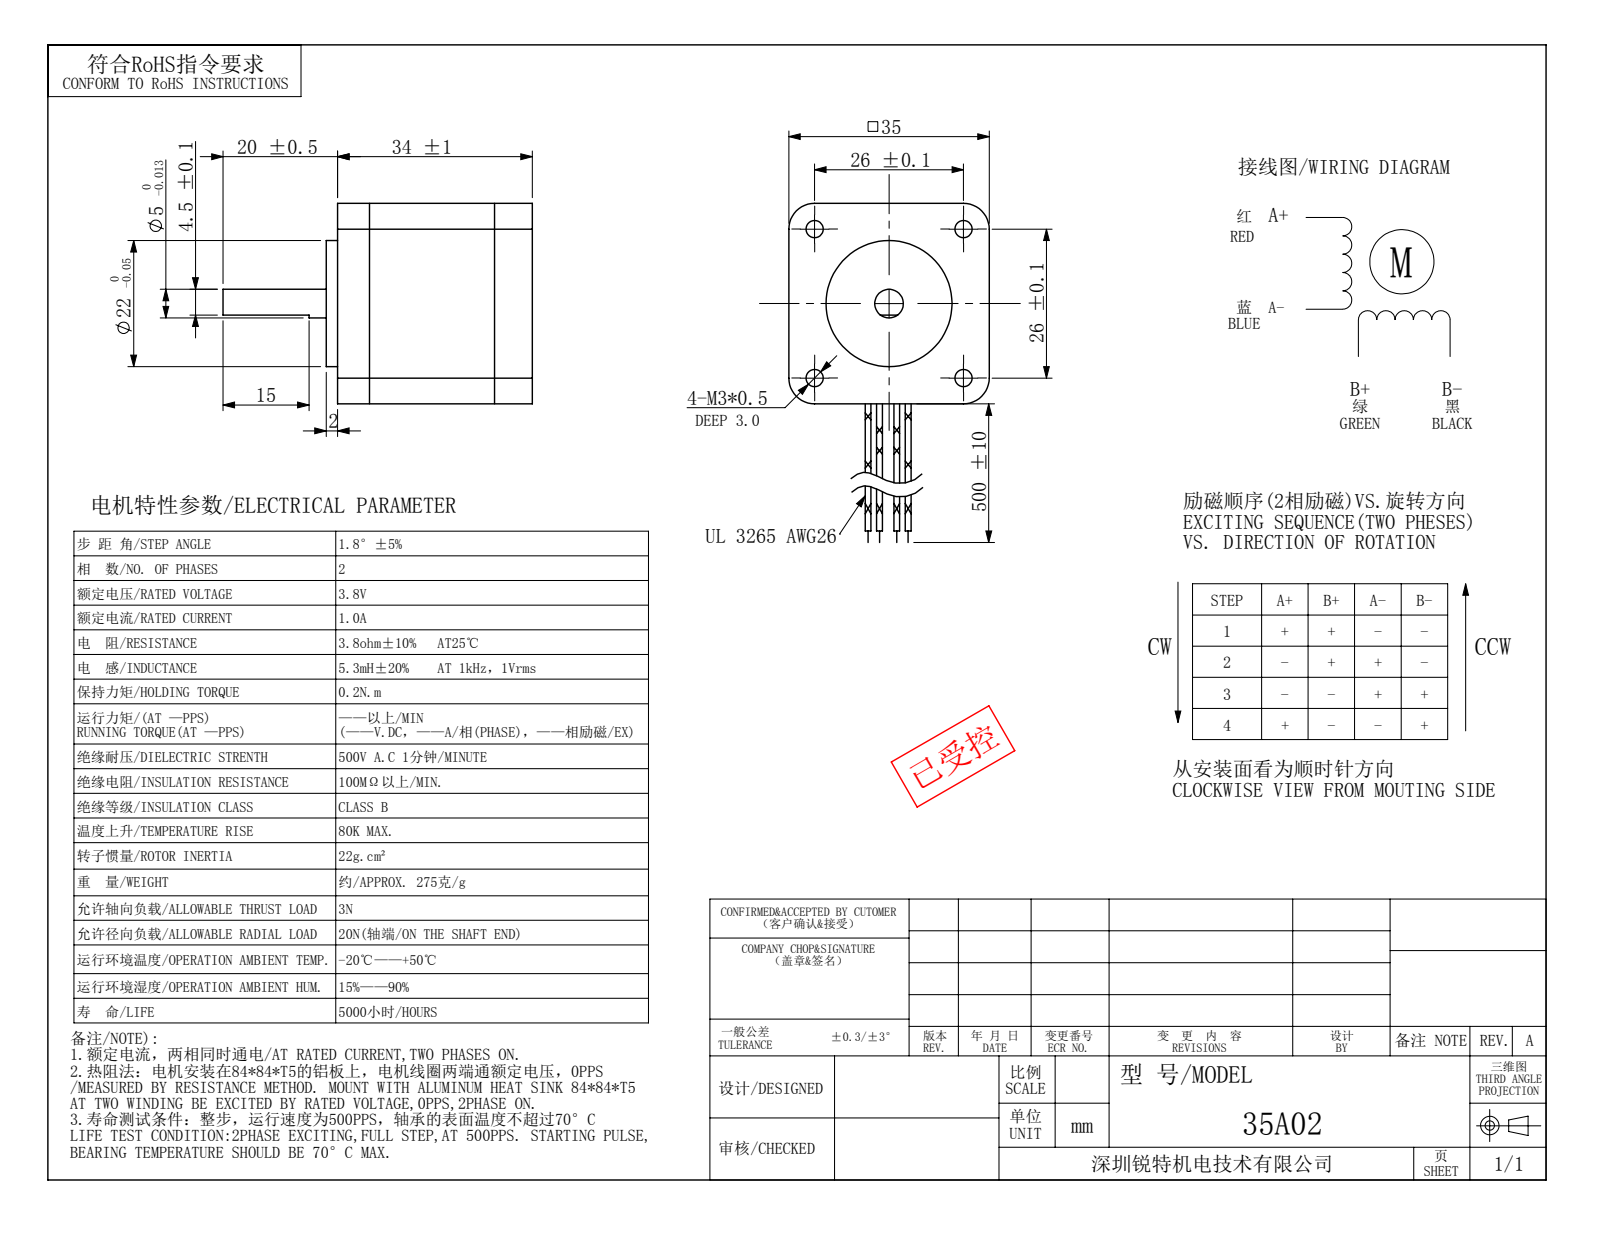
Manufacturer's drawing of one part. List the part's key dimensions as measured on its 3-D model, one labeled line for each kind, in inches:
Part name (STEP PRODUCT): 35HS34-D0520-001
STEP written by: SolidWorks 2014 (AUTOMOTIVE_DESIGN)
Units: inches
Bodies: 1 solid, 30 faces (14 planar, 16 cylindrical, 0 other)
Overall size (bounding box): 2.126 × 1.378 × 1.378
Volume: 2.567 in³ · Surface area: 11.54 in²
Round holes (diameter × count): ⌀0.118 ×4
Round bosses / shafts (diameter × count): ⌀0.866 ×1, ⌀0.197 ×1
Partial cylindrical surfaces — rounded edges, fillets, slot ends (radius × count): R0.177 ×4
Main face-to-face distances: 1.378, 1.339, 1.417, 0.079, 0.768, 0.61, 0.118, 0.197, 1.22, 2.126
Hole centre spacings: 1.024, 1.448
